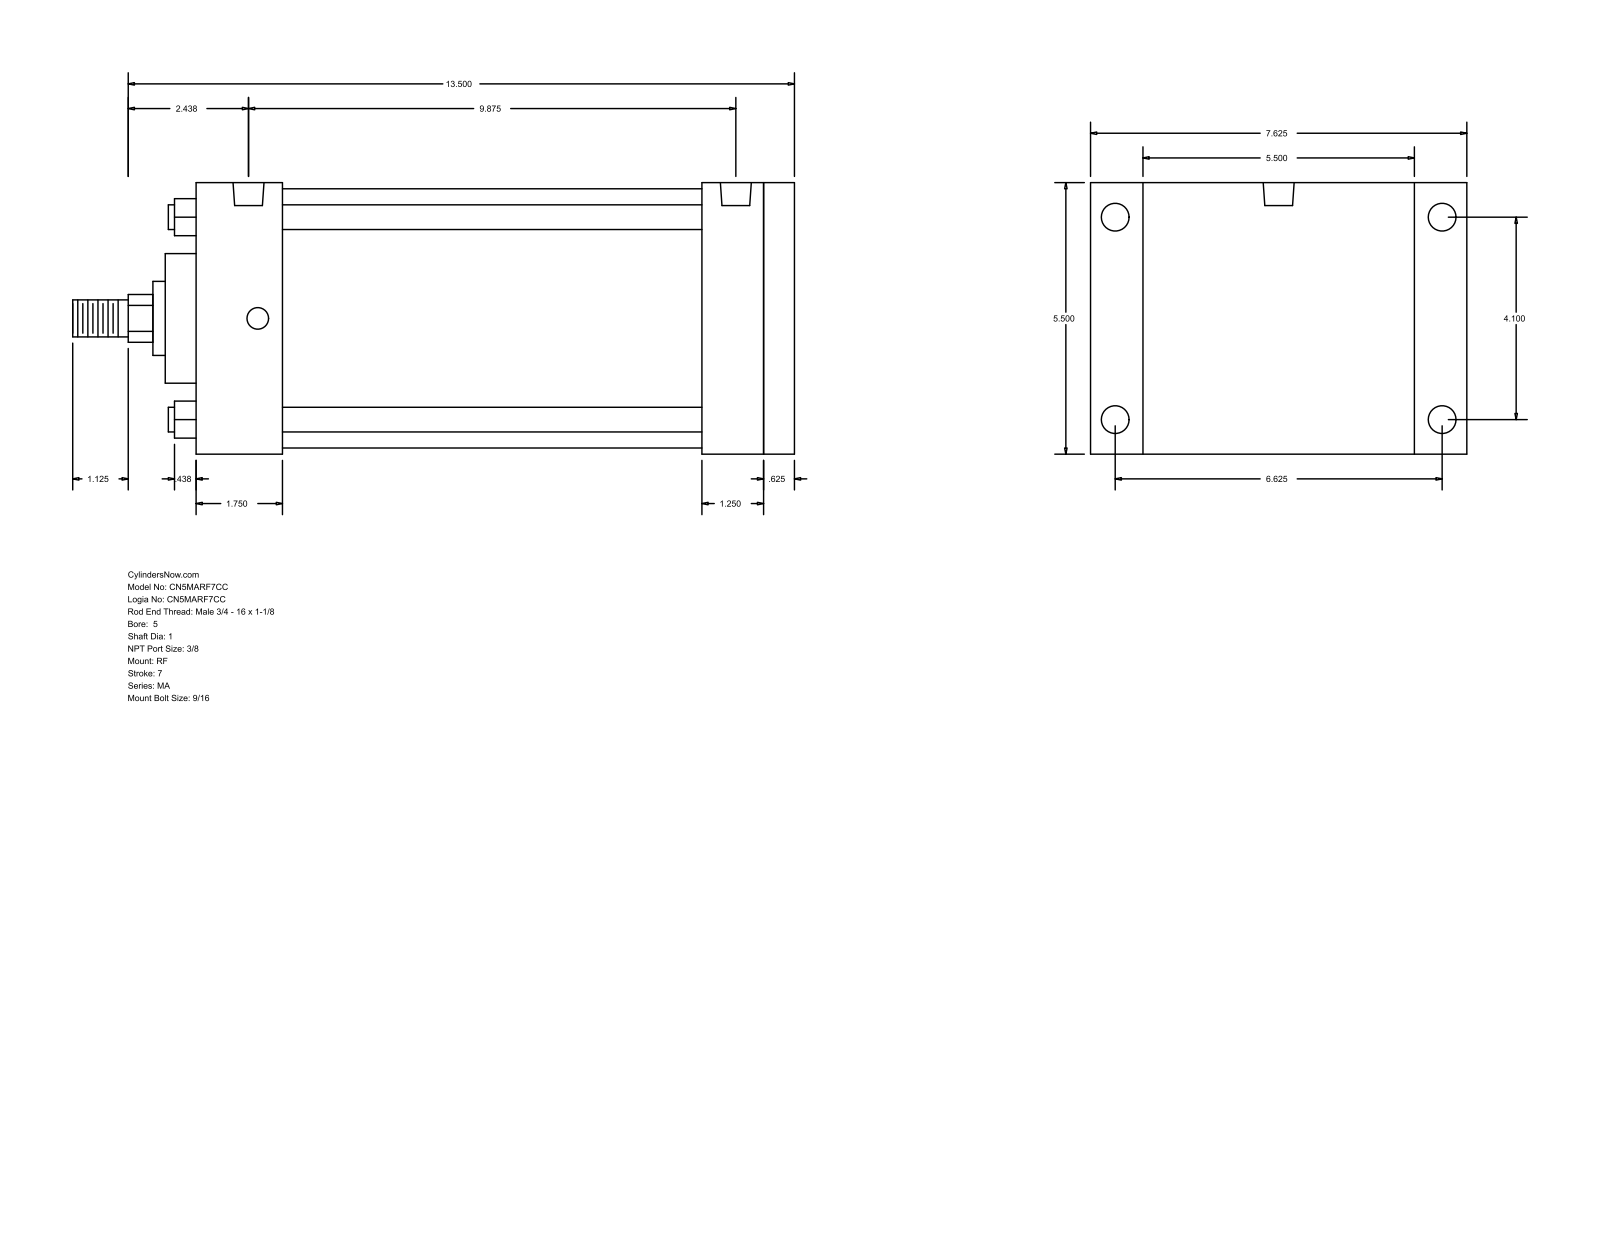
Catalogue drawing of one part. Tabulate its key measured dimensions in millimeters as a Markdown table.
| quantity | value |
| --- | --- |
| part name | MA_RF__0500_1 |
| STEP written by | GSSL Pune (CONFIG_CONTROL_DESIGN) |
| units | millimeters |
| bodies | 0 solids, 94 faces (65 planar, 29 cylindrical, 0 other) |
| overall size | 371.48 × 193.68 × 139.7 |
| round holes (diameter × count) | 11.11 × 4, 14.29 × 4, 15.93 × 2 |
| round bosses / shafts (diameter × count) | 12.7 × 4, 133.35 × 1, 66.67 × 1, 38.1 × 1, 25.4 × 1, 19.05 × 1 |
| partial cylindrical surfaces (radius × count) | 12.29 × 1 |
| main face-to-face distances | 139.7, 307.98, 292.1, 15.88, 44.46, 247.64, 263.52, 260.35, 215.89, 31.75 |
| hole center spacings | 4.76, 104.14, 168.28, 197.9, 241.31, 246.07, 250.83 |
